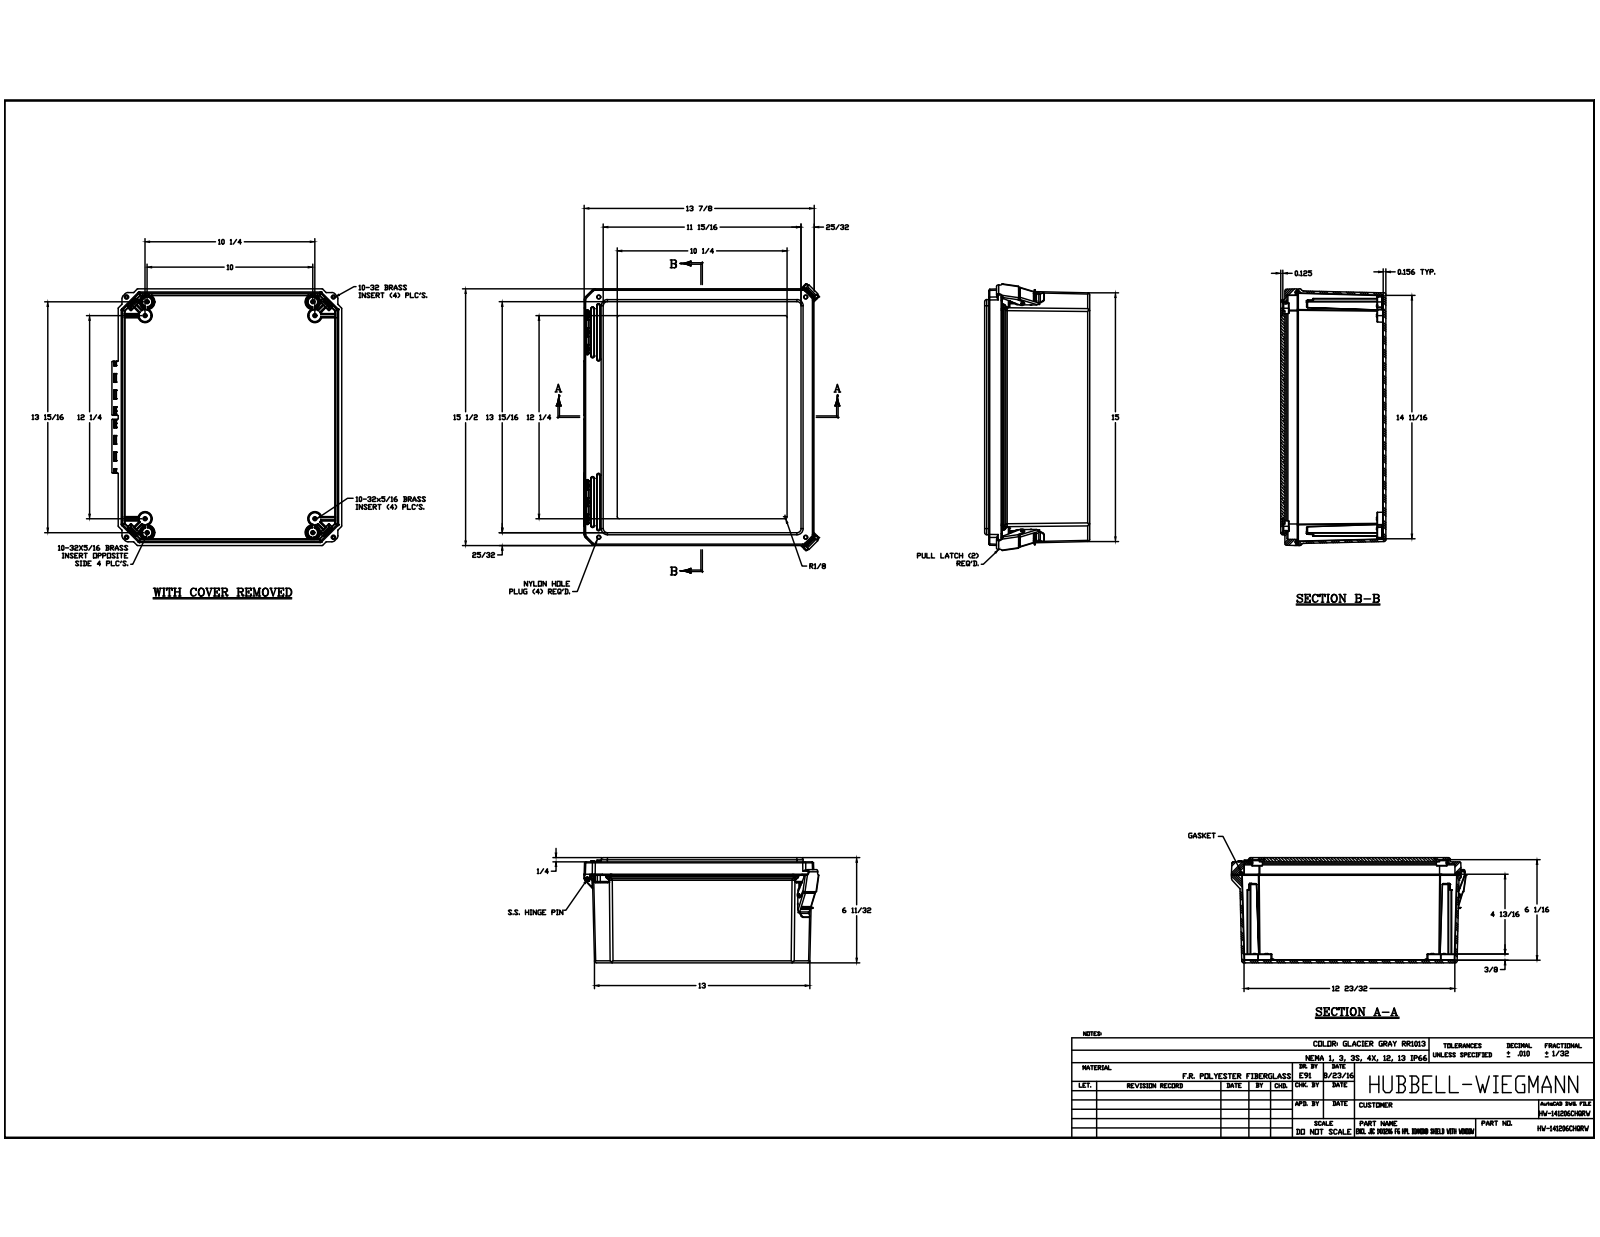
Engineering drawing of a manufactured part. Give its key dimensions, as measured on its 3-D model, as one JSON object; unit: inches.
{"part_name": "DSW141206HPL_STP; DS141206BOX; BRASS INSERT-(; BRASS INSERT-(_1 (+8 more)", "step_written_by": "Autodesk Inventor 2017 (AUTOMOTIVE_DESIGN)", "units": "inches", "bodies": {"solids": 34, "faces": 2322, "planar": 818, "cylindrical": 924, "other": 580}, "overall_size": [16.131, 14.189, 6.341], "volume_in3": 135.2, "surface_area_in2": 1676, "round_holes": [[0.156, 16], [0.152, 8], [0.135, 6], [0.15, 4], [0.252, 4], [0.253, 4], [0.135, 2], [0.219, 2], [0.227, 2], [0.313, 2], [0.375, 2], [0.137, 1]], "round_bosses_or_shafts": [[0.246, 16], [0.87, 4], [0.3, 4], [0.209, 4], [0.435, 2], [0.135, 1]], "partial_cylinders_radius": [[0.01, 178], [0.005, 88], [0.03, 65], [0.02, 49], [0.06, 35], [0.063, 27], [0.09, 26], [0.125, 26]], "face_to_face_distances": [0.156, 6.185, 6.341, 6.117, 5.961, 0.225, 0.14, 0.139, 0.125, 0.25], "hole_center_spacings": [1.582, 10.16, 0.25, 0.841, 1.277, 11.248, 11.425, 13.081]}
